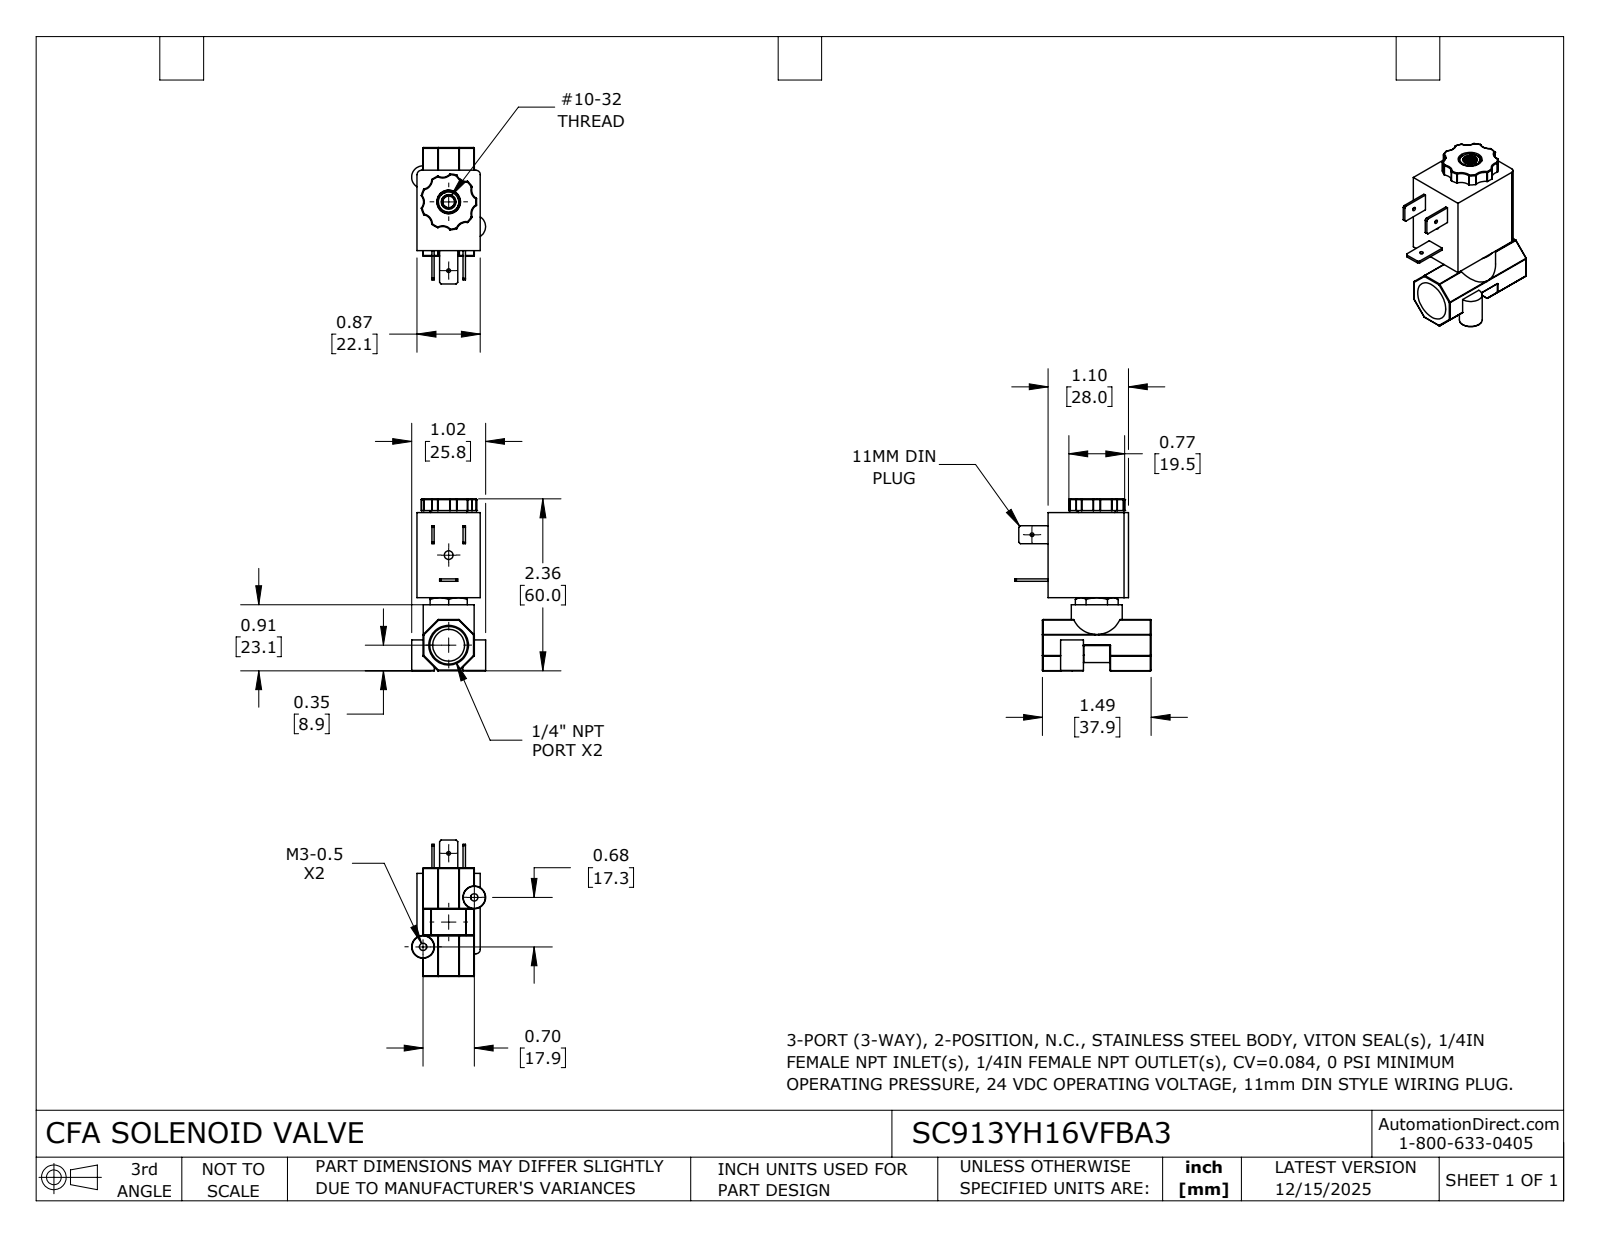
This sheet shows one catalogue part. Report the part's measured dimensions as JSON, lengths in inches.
{"part_name": "SC913YH16VFBA3", "step_written_by": "SolidWorks 2024 (CONFIG_CONTROL_DESIGN)", "units": "inches", "bodies": {"solids": 1, "faces": 308, "planar": 68, "cylindrical": 139, "other": 101}, "overall_size": [2.363, 1.874, 1.017], "volume_in3": 1.665, "surface_area_in2": 16.1, "round_holes": [[0.05, 2], [0.1, 2], [0.12, 1], [0.16, 1], [0.327, 1], [0.438, 1]], "round_bosses_or_shafts": [[0.313, 2], [0.7, 1], [0.315, 1]], "partial_cylinders_radius": [[0.01, 42], [0.005, 14], [0.133, 7], [0.06, 2], [0.132, 2], [0.237, 1], [0.306, 1], [0.385, 1]], "face_to_face_distances": [0.87, 0.704, 1.104, 1.167, 0.083, 0.787, 1.006, 2.173, 2.363, 1.357], "hole_center_spacings": [0.489, 0.7, 0.945, 0.979, 1.238, 1.333]}
